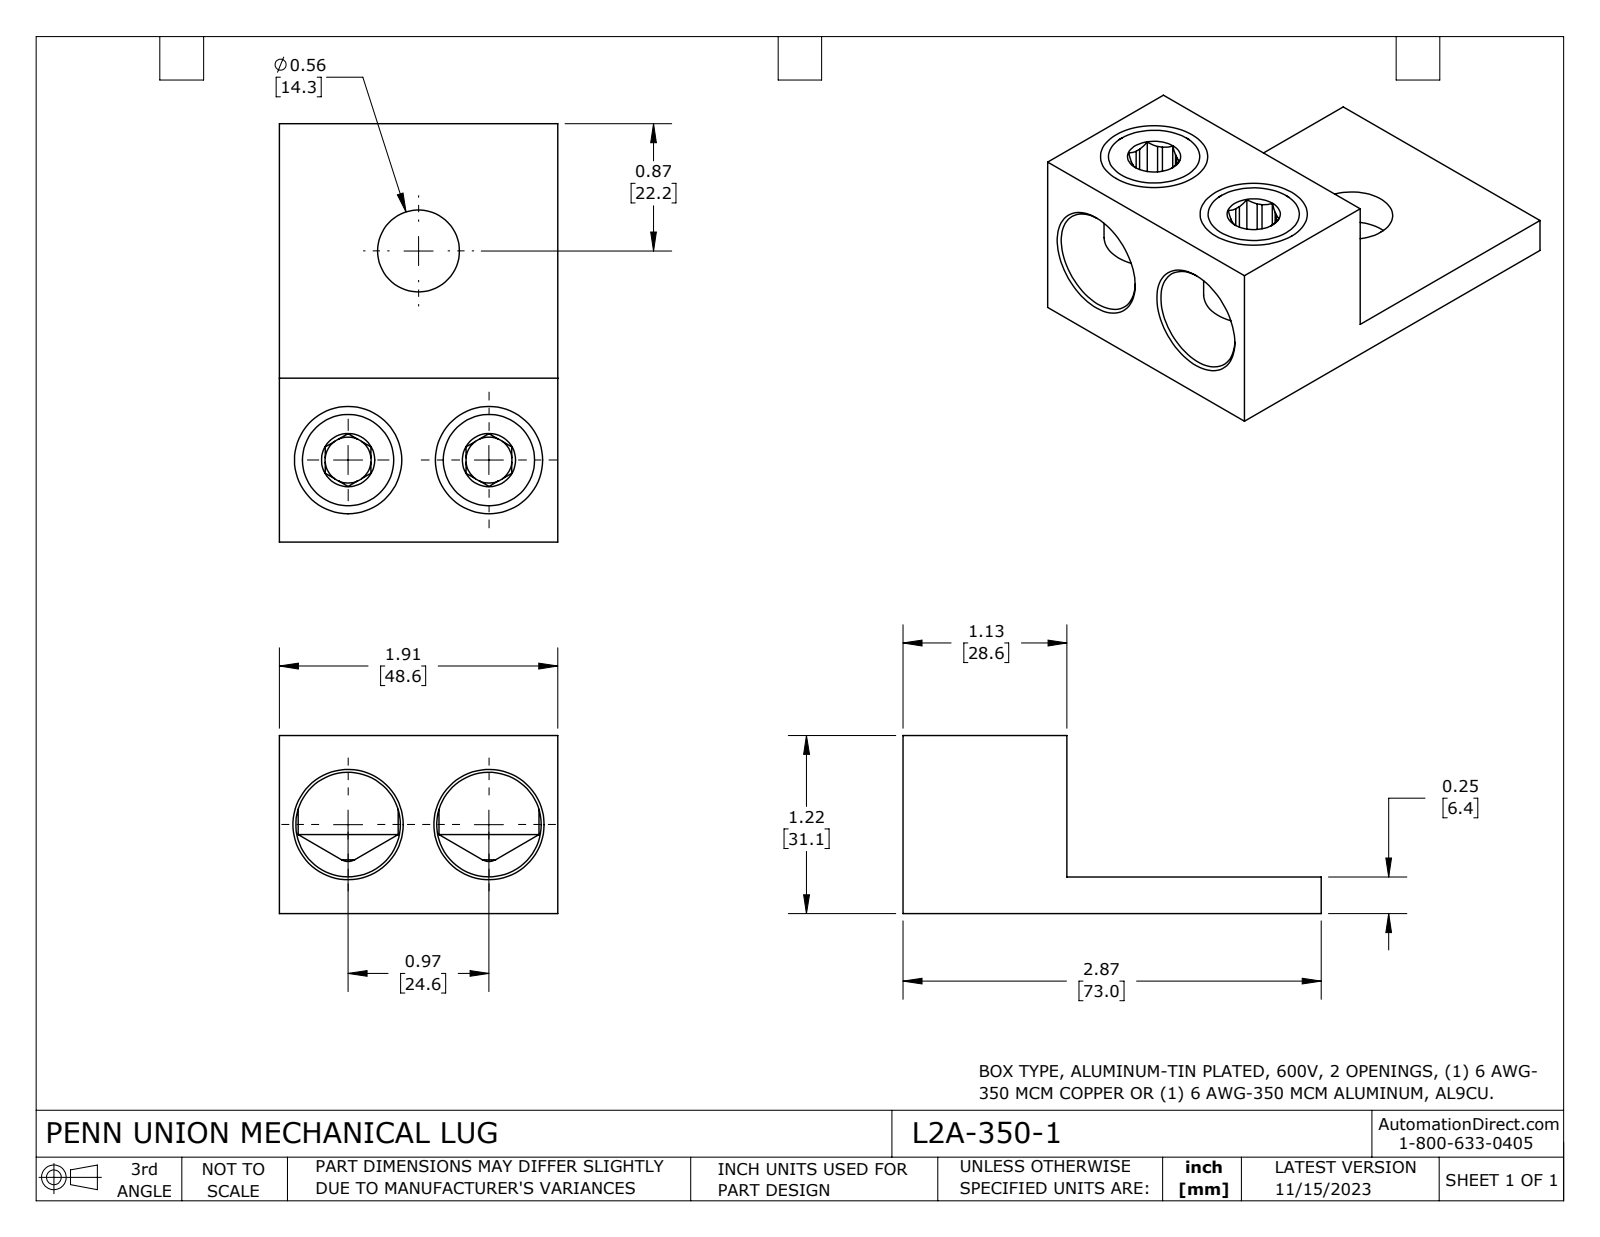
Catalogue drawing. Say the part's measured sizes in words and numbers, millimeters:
The part is named "L2A-350-1". Its 3-D file was written by "SolidWorks 2023 (CONFIG_CONTROL_DESIGN)". It is 3 solids with 90 faces: 46 planar, 18 cylindrical and 26 other. Overall it measures 73 by 48.6 by 31.1 millimeters. Its volume is 45 670 cubic millimeters and its surface area 18 090 square millimeters. Round holes: 2 of diameter 8, 2 of diameter 15.9, 2 of diameter 18.3, 1 of diameter 14.3. Round bosses or shafts: 2 of diameter 17.4. The main face-to-face distances are 6.4, 48.6, 31.1, 24.7, 28.6, 73, 44.4, 8, 12.3, 8. The hole center spacings are 24.6, 38.5.
